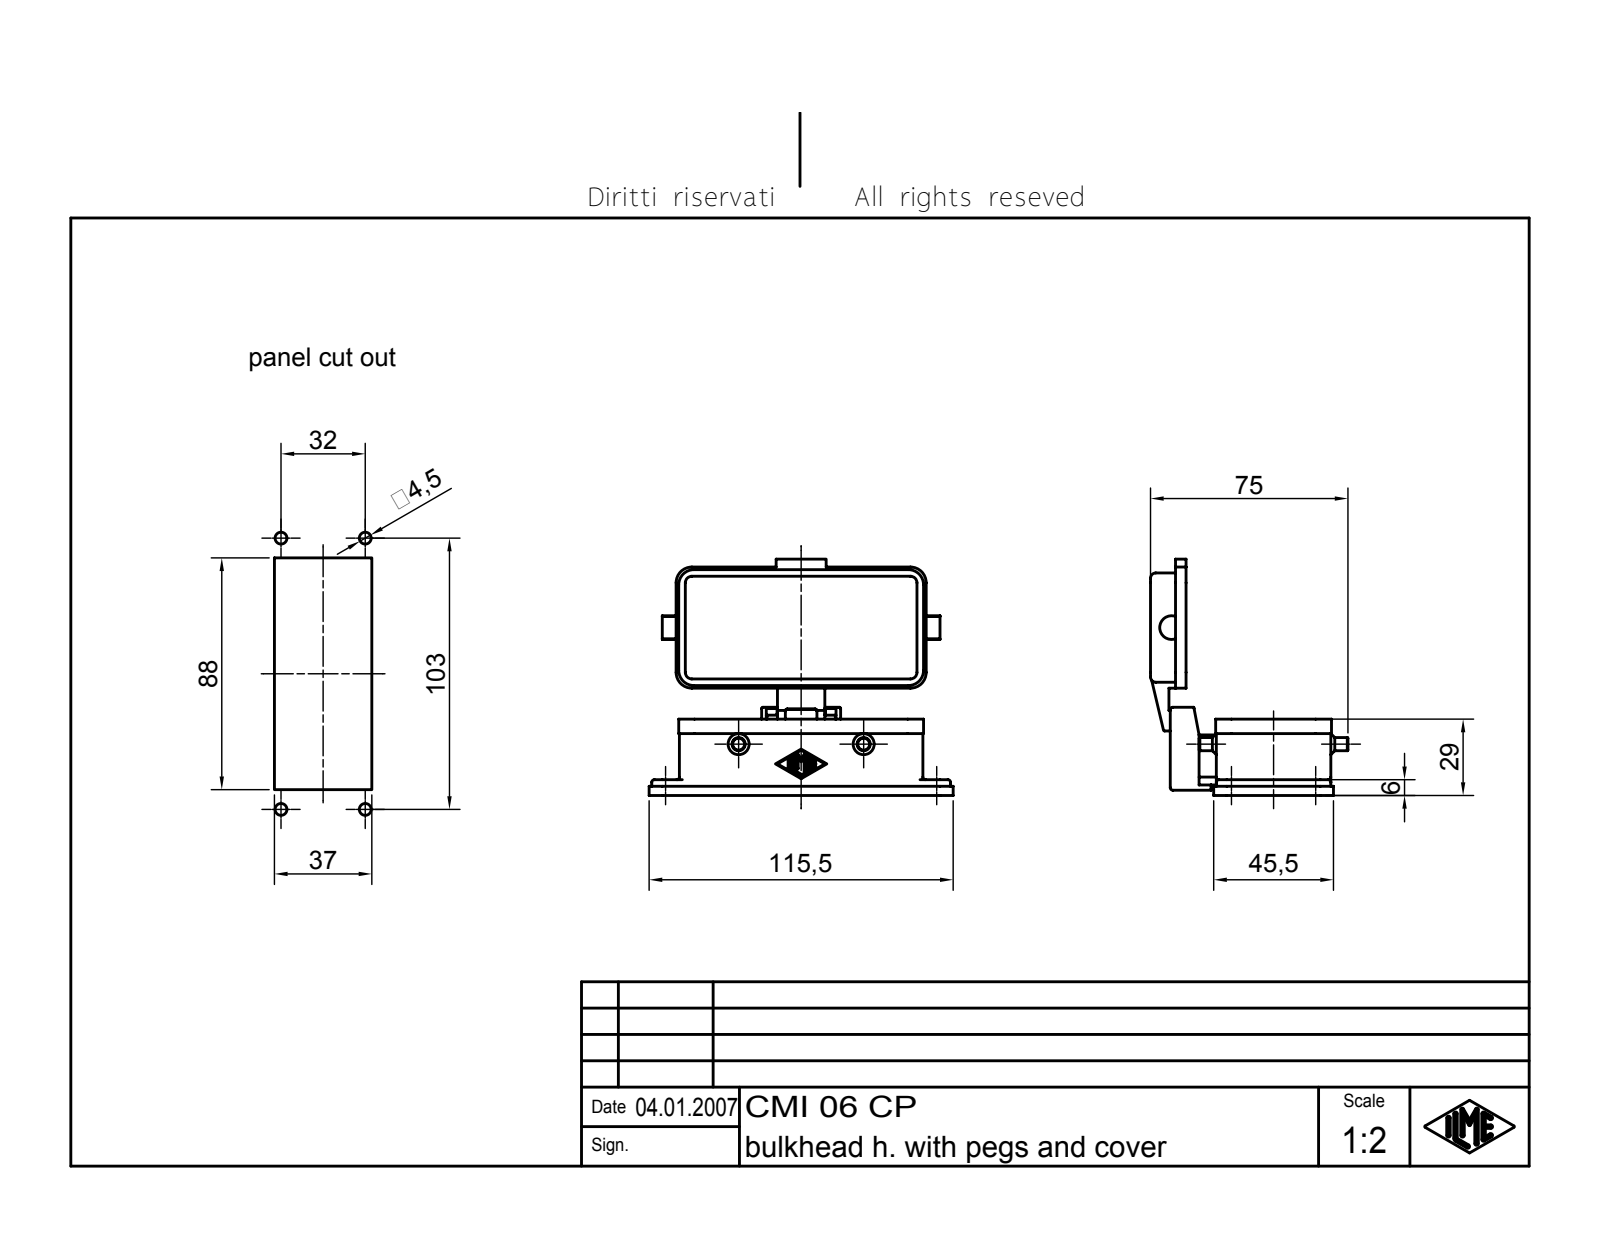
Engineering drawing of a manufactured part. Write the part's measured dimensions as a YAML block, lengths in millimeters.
part_name: "CMI 06 CP"
step_written_by: "Autodesk Inventor 7 (AUTOMOTIVE_DESIGN)"
units: millimeters
bodies: {solids: 1, faces: 470, planar: 205, cylindrical: 179, other: 86}
overall_size: [115.5, 89.75, 75]
volume: 56542
surface_area: 42153
round_holes:
  - {diameter: 4.5, count: 4}
  - {diameter: 4.6, count: 4}
  - {diameter: 4, count: 1}
  - {diameter: 5, count: 1}
round_bosses_or_shafts:
  - {diameter: 5, count: 2}
  - {diameter: 3, count: 2}
  - {diameter: 7, count: 1}
  - {diameter: 4, count: 1}
partial_cylinders:
  - {radius: 0.38, count: 14}
  - {radius: 6, count: 12}
  - {radius: 0.5, count: 10}
  - {radius: 0.7, count: 8}
  - {radius: 1, count: 8}
  - {radius: 2, count: 8}
  - {radius: 2.5, count: 8}
  - {radius: 3, count: 4}
face_to_face_distances: [2.5, 3, 4, 40.5, 0.75, 1.25, 40.75, 1, 2, 25.5]
hole_center_spacings: [32, 103, 107.86]
